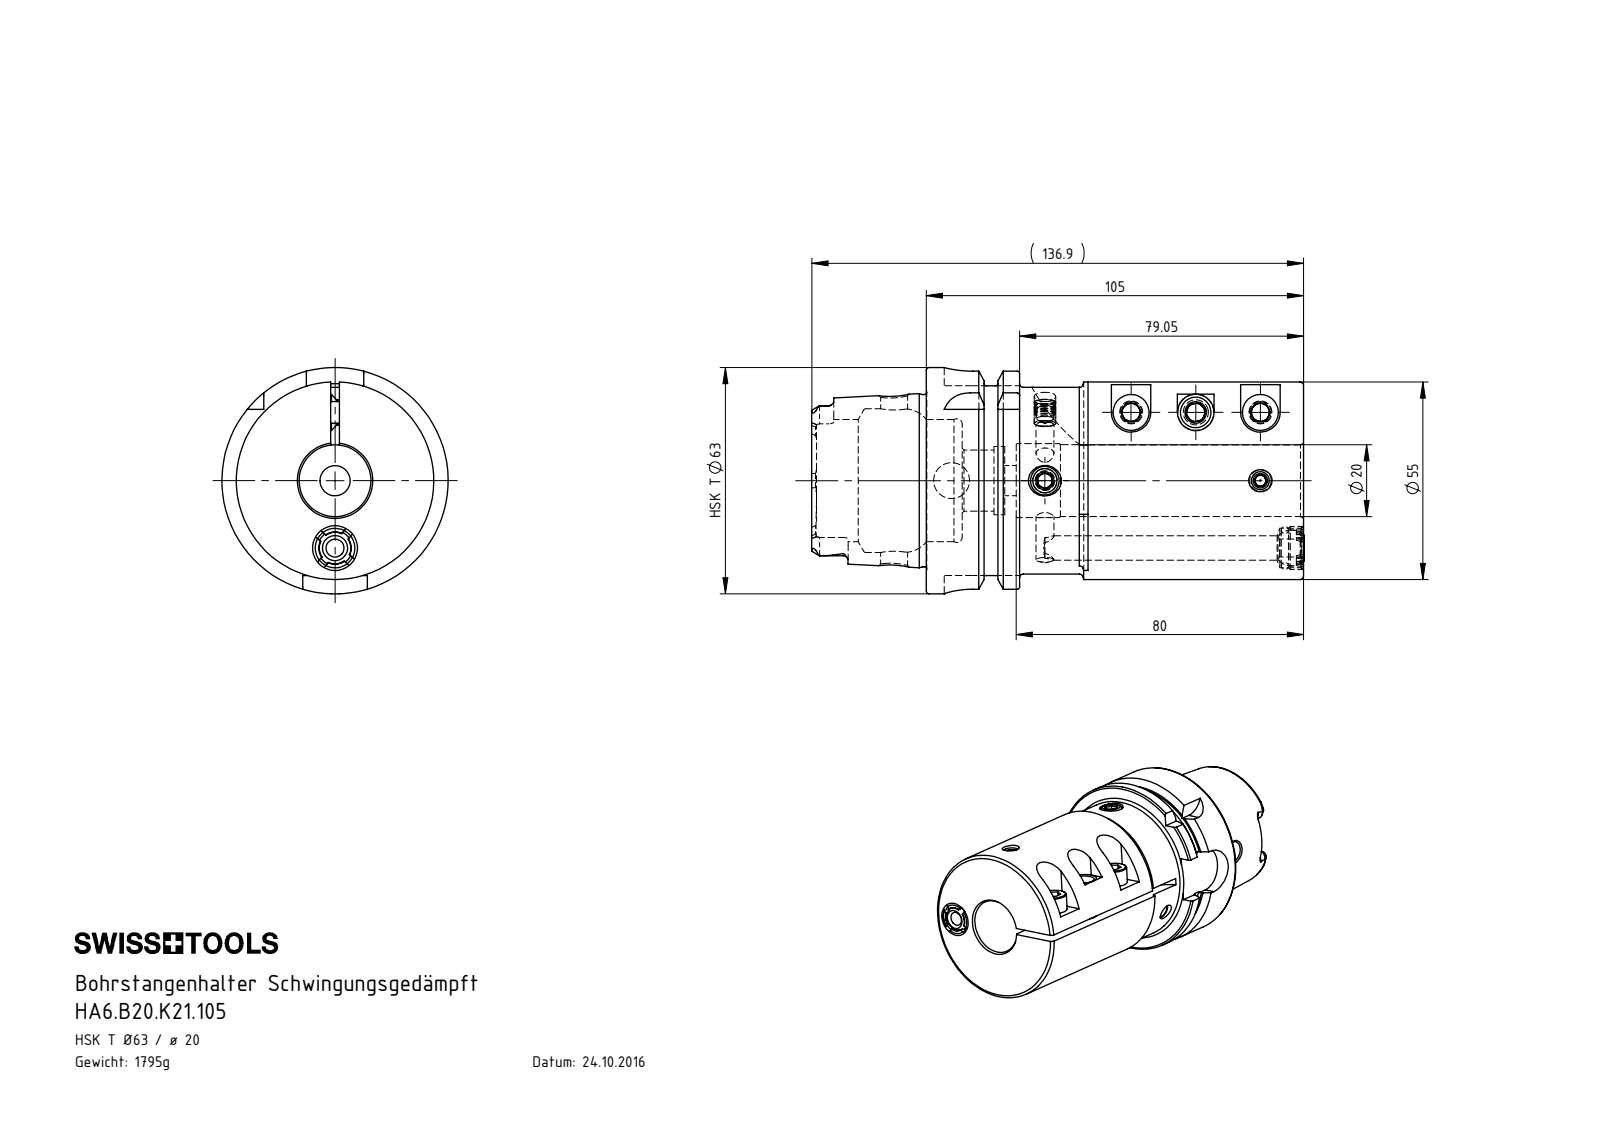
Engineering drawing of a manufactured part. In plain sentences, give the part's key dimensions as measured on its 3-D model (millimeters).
The part is named "KU1-U12.002.010_A; HA6-B20.K21.105_A; KVT_MB_600_060; ISO 4028 - M10 x 16 (+7 more)". Its 3-D file was written by "SolidWorks 2015 (CONFIG_CONTROL_DESIGN)". It is 11 solids with 478 faces: 158 planar, 125 cylindrical and 195 other. Overall it measures 137.39 by 63 by 63 millimeters. Its volume is 228 762 cubic millimeters and its surface area 52 542 square millimeters. Round holes: 5 of diameter 5, 2 of diameter 6.4, 2 of diameter 6.8, 2 of diameter 10, 1 of diameter 4, 1 of diameter 7.5, 1 of diameter 8.4, 1 of diameter 8.5, 1 of diameter 11, 1 of diameter 17, 1 of diameter 19, 1 of diameter 20. Round bosses or shafts: 4 of diameter 6, 3 of diameter 10, 1 of diameter 63, 1 of diameter 55, 1 of diameter 54.95, 1 of diameter 52, 1 of diameter 47.94, 1 of diameter 12. Partial cylindrical surfaces (rounded edges, fillets, slot ends): 6 of radius 1.4, 4 of radius 2.88, 4 of radius 8, 2 of radius 5.5, 1 of radius 4.4, 1 of radius 5.1, 1 of radius 52, 1 of radius 55. The main face-to-face distances are 2.4, 105, 45, 60, 42.6, 62.4, 16, 25.95, 16.65, 19.05. The hole center spacings are 18, 18.75, 19, 26, 26.17, 30.61, 36, 40.71.
